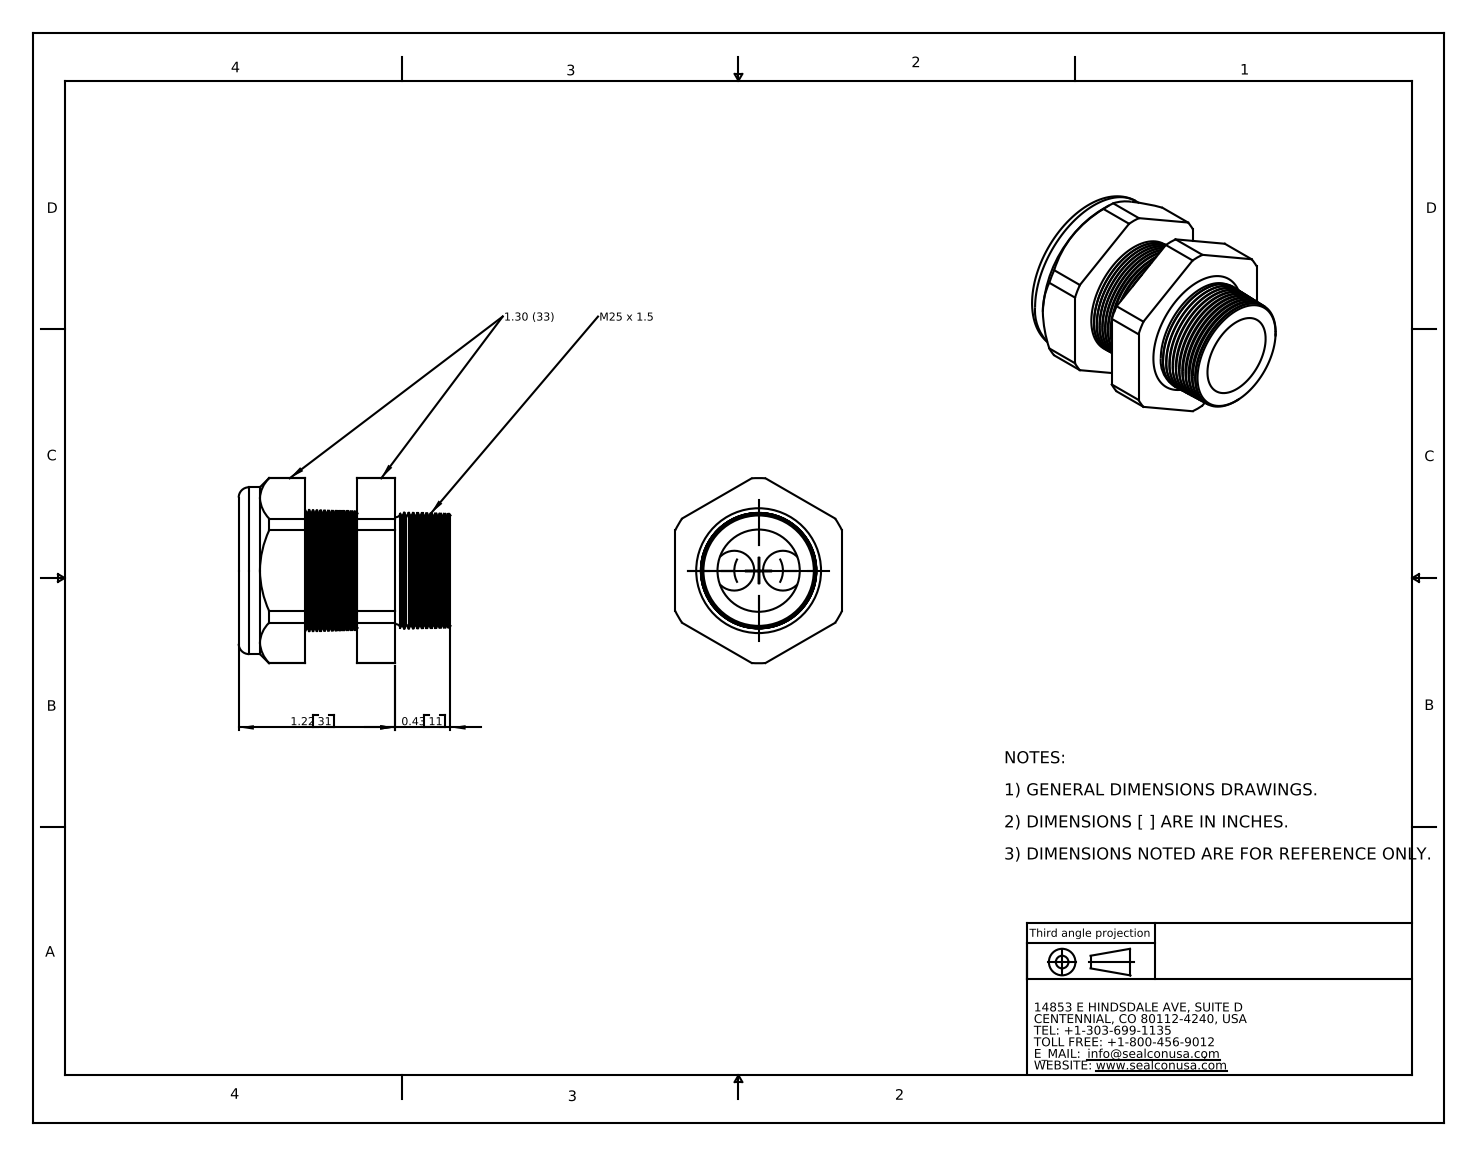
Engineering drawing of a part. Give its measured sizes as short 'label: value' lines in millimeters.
name: CD25M3-BK
written by: SolidWorks 2007 (CONFIG_CONTROL_DESIGN)
unit: mm
bodies: 2 solids, 210 faces (20 planar, 24 cylindrical, 166 other)
size: 41.9 × 36.7 × 33
volume: 18 700 mm³; area: 10 900 mm²
holes: 2× ⌀7.9, 1× ⌀17.5, 1× ⌀18
bosses: 1× ⌀33
rounds: 1× R18.3
face distances: 33, 10.3, 17.8, 7.5, 13.2, 23.5, 31, 41.9, 28.7, 18.4
hole spacings: 4.8, 9.6
